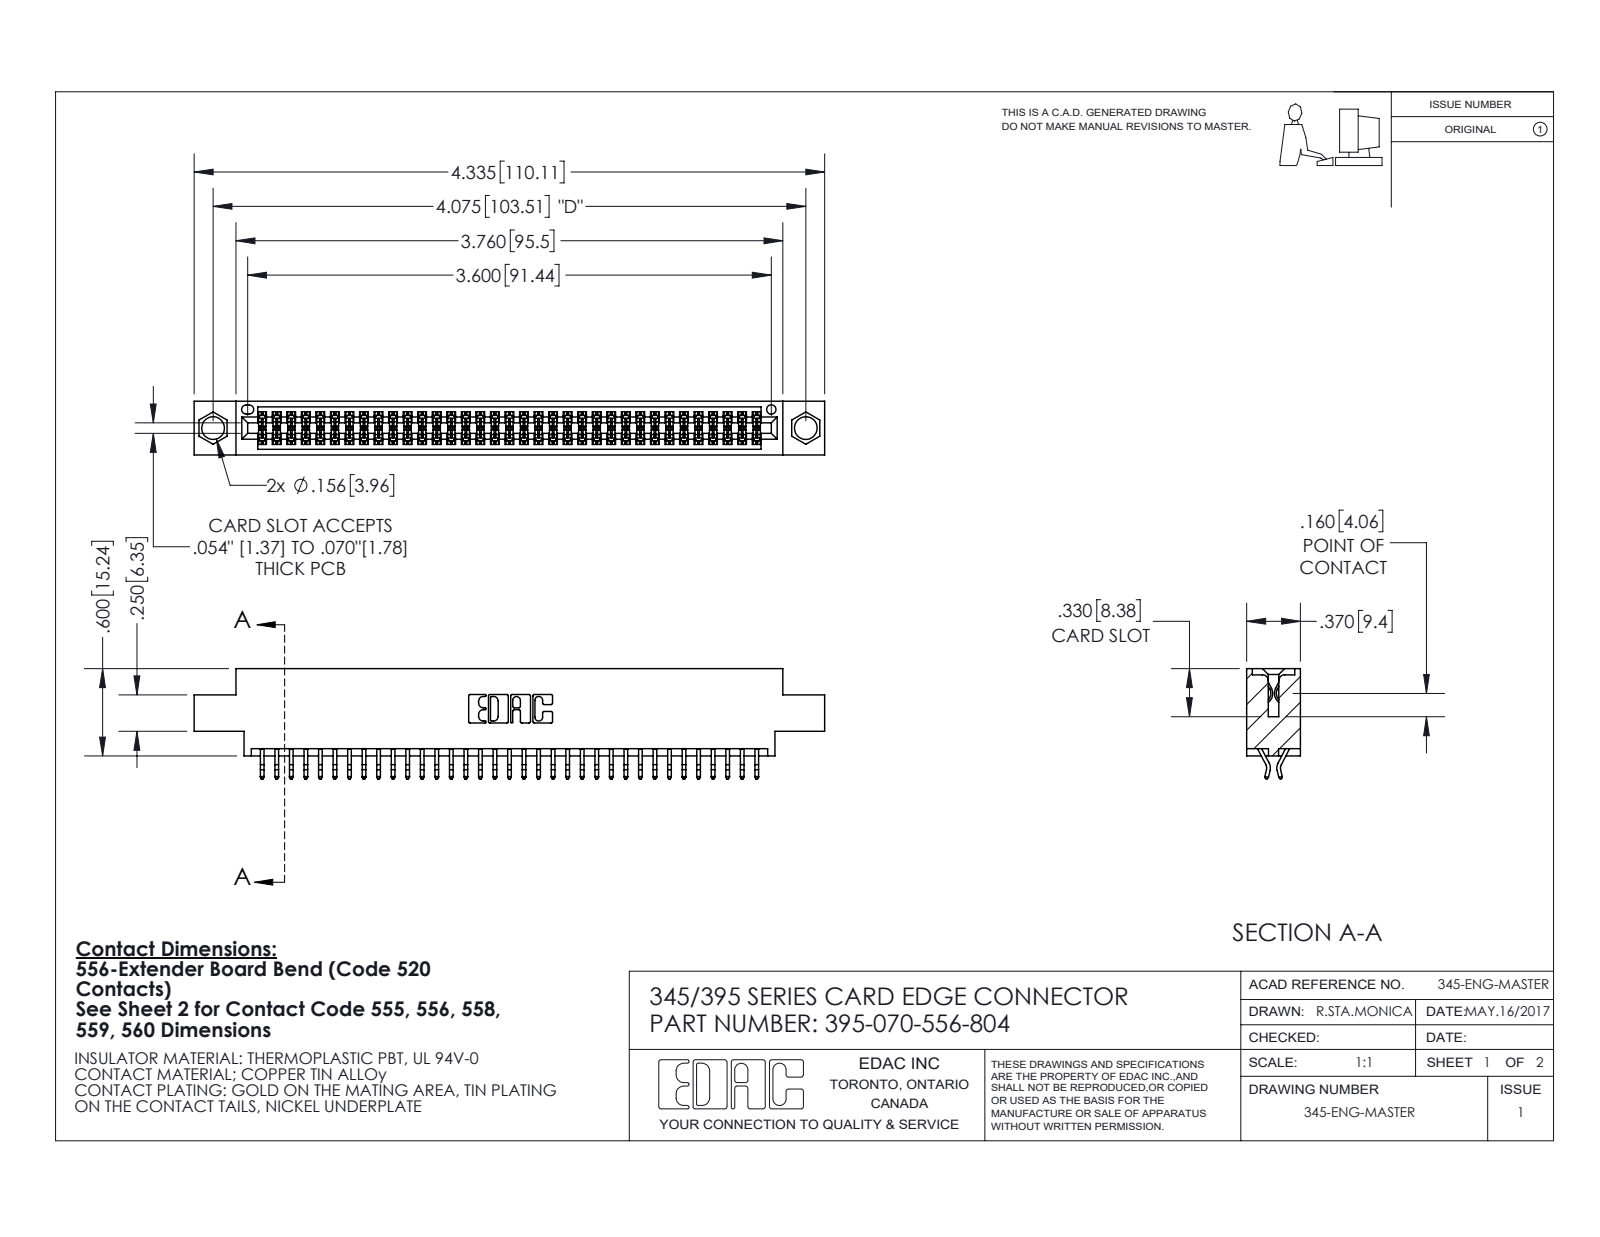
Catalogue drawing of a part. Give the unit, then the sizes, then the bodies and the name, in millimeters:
Units: millimetres
Overall size (bounding box): 110.1 × 19.2 × 9.4
Round holes (diameter × count): ⌀4 ×2, ⌀1.6 ×1
Partial cylindrical surfaces — rounded edges, fillets, slot ends (radius × count): R0.2 ×105, R0.3 ×22, R0.2 ×6, R0.8 ×6, R0.7 ×3, R0.3 ×2, R0.4 ×2, R0.5 ×2
Main face-to-face distances: 7.6, 1.8, 9.4, 5.1, 0.6, 2.5, 6.9, 5.7, 4.4, 3.8
Hole centre spacings: 6.9, 97.5, 103.5
Volume: 10 400 mm³ · Surface area: 15 190 mm²
Bodies: 71 solids, 4064 faces (2688 planar, 1376 cylindrical, 0 other)
Part name (STEP PRODUCT): 345-292-001_556 Tail; 395-070-556-804; 345 Part_0.170 Offset - 0.156 Dia-TI
STEP written by: SolidWorks 2020 (CONFIG_CONTROL_DESIGN)
